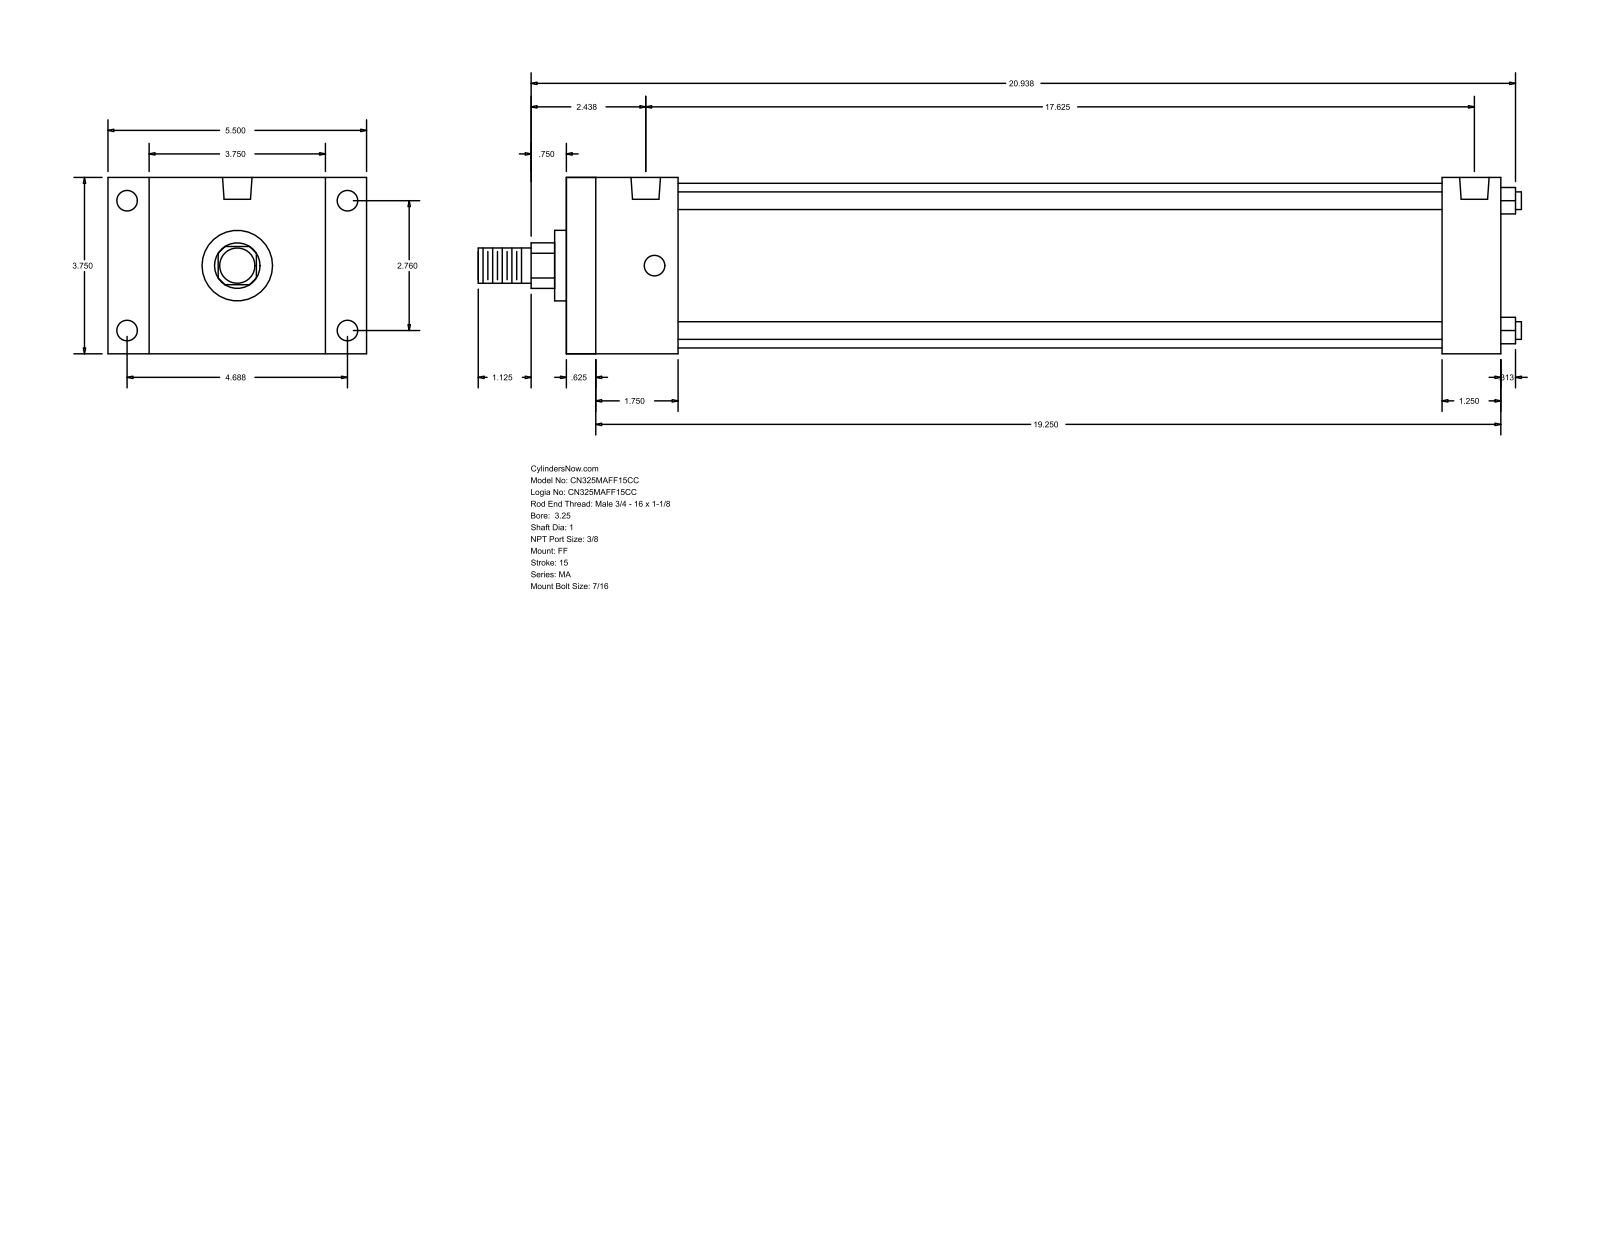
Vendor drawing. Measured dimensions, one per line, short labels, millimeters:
name: MA_FF__0325_1
written by: GSSL Pune (CONFIG_CONTROL_DESIGN)
unit: mm
bodies: 0 solids, 92 faces (64 planar, 28 cylindrical, 0 other)
size: 563.56 × 139.7 × 95.25
holes: 8× ⌀11.11, 2× ⌀15.93
bosses: 4× ⌀9.53, 1× ⌀88.9, 1× ⌀38.1, 1× ⌀25.4, 1× ⌀19.05
rounds: 1× R12.29
face distances: 95.24, 504.83, 15.87, 488.96, 22.23, 117.47, 60.33, 473.07, 44.46, 457.2
hole spacings: 70.1, 119.06, 138.16, 438.15, 4.76, 4.77, 442.91, 442.92
